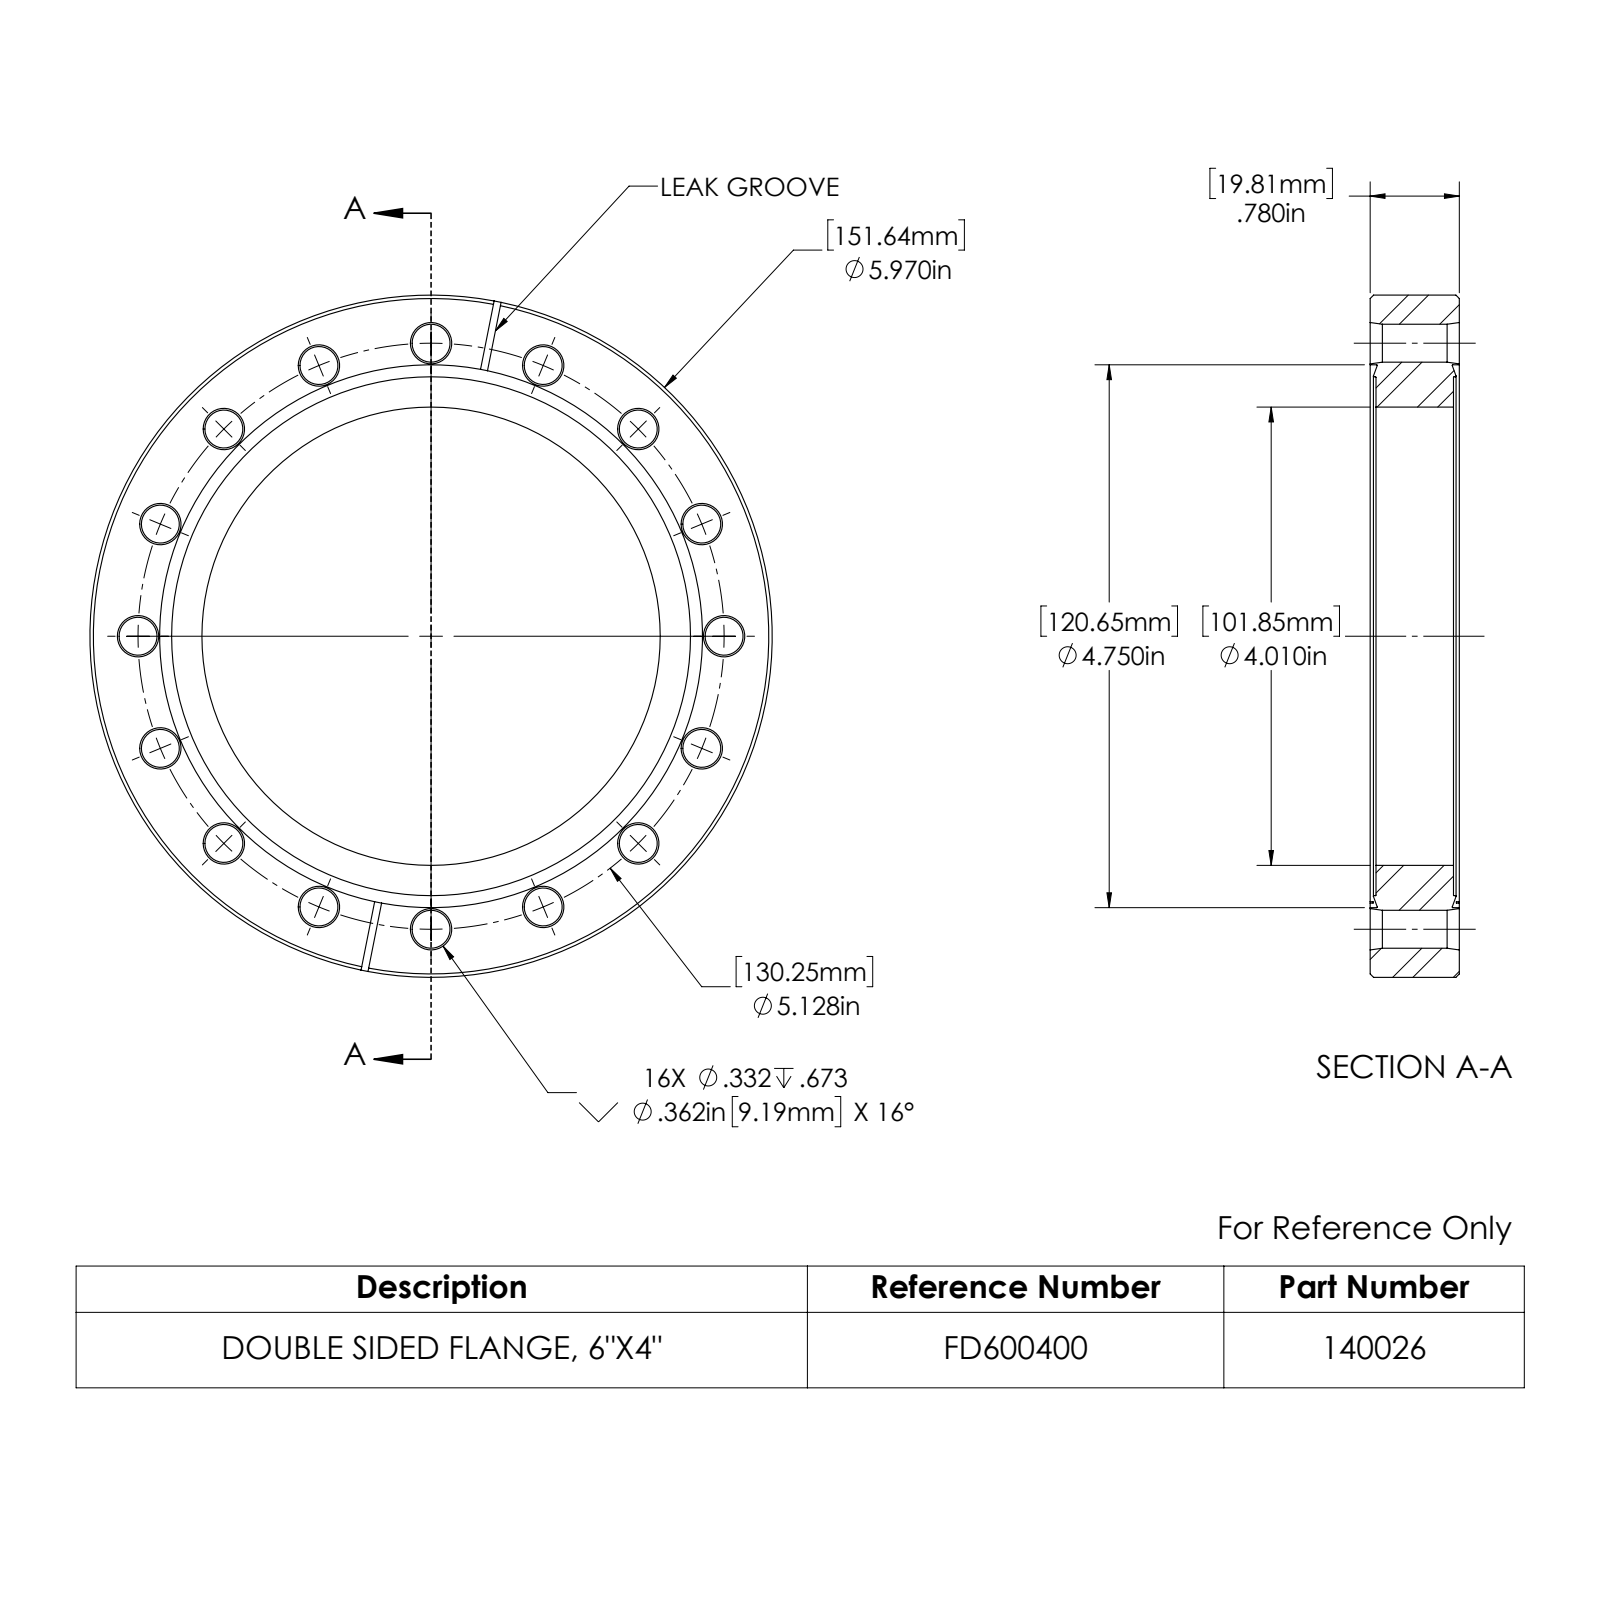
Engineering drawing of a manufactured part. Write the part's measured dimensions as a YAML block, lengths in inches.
part_name: "140026_A"
step_written_by: "SolidWorks 2022 (CONFIG_CONTROL_DESIGN)"
units: inches
bodies: {solids: 1, faces: 148, planar: 14, cylindrical: 48, other: 86}
overall_size: [5.97, 5.97, 0.78]
volume: 10.34
surface_area: 66.15
round_holes:
  - {diameter: 0.332, count: 16}
  - {diameter: 4.01, count: 1}
  - {diameter: 4.54, count: 1}
  - {diameter: 4.75, count: 1}
round_bosses_or_shafts:
  - {diameter: 5.97, count: 1}
partial_cylinders:
  - {radius: 1.25, count: 4}
face_to_face_distances: [0.78, 0.729, 0.051, 0.051, 0.678, 0.729, 0.062, 0.061, 0.063]
hole_center_spacings: [1, 4.264, 4.738, 5.03, 1.963, 2.564, 3.626, 2.849]
